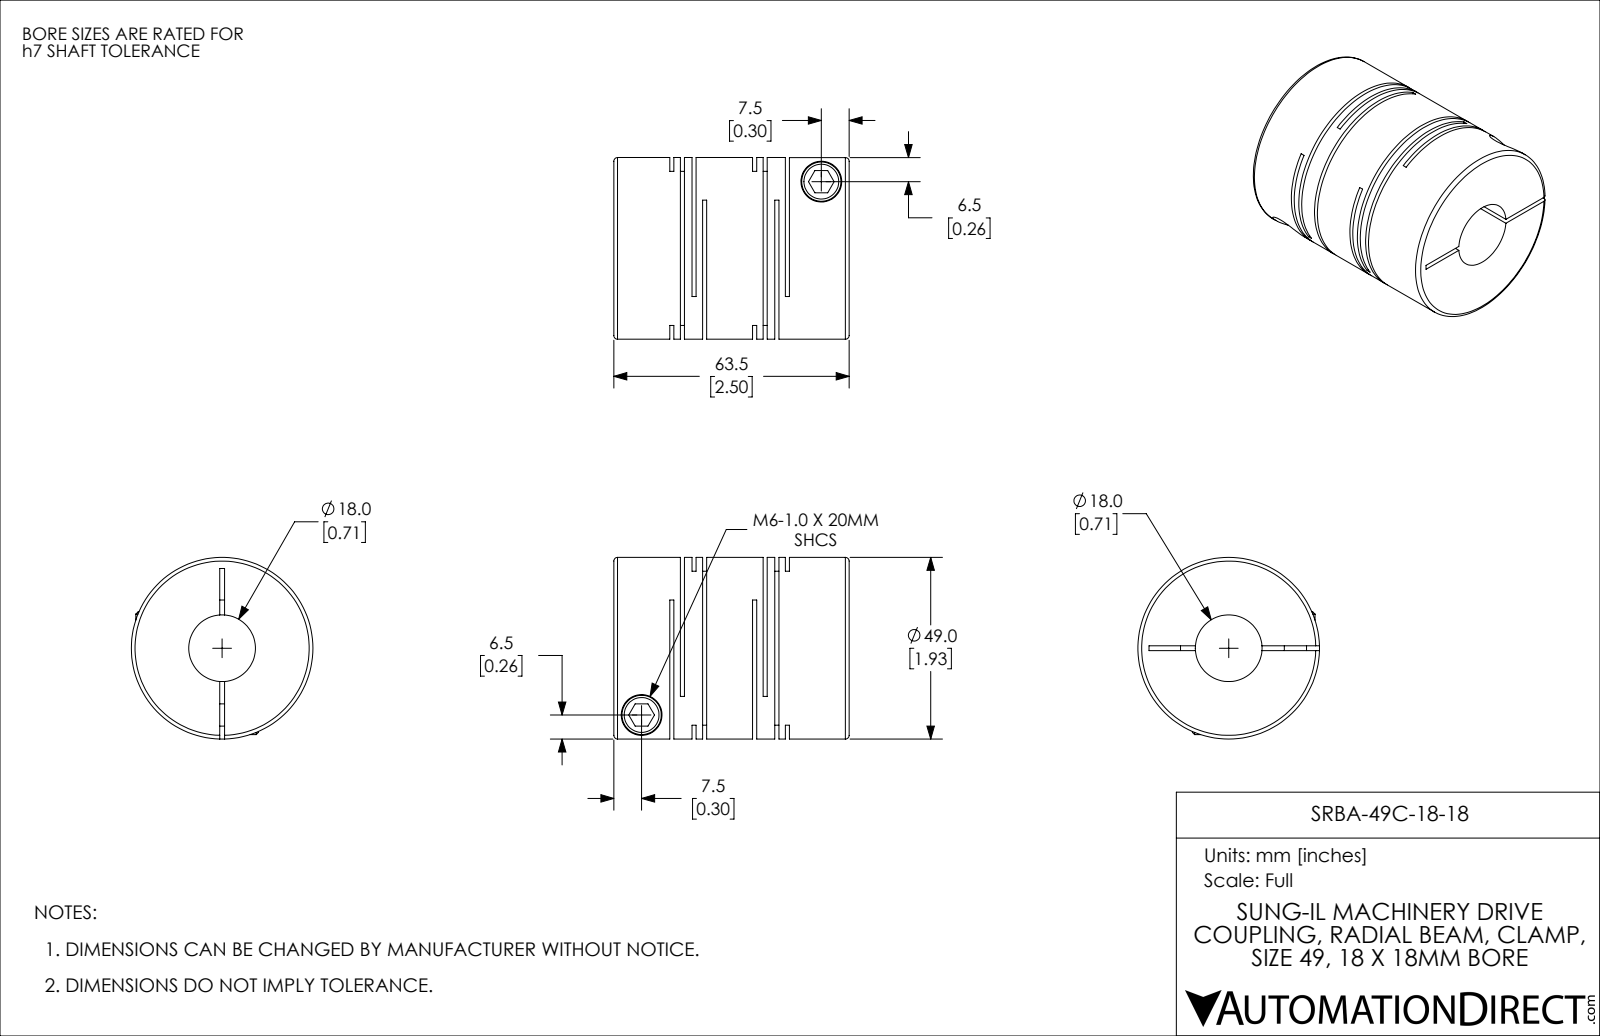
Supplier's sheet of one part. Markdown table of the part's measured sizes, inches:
| quantity | value |
| --- | --- |
| part name | SRBA-49C-18-18 |
| STEP written by | SolidWorks 2021 (CONFIG_CONTROL_DESIGN) |
| units | inches |
| bodies | 1 solid, 114 faces (60 planar, 42 cylindrical, 12 other) |
| overall size | 2.5 × 1.929 × 1.929 |
| volume | 5.456 in³ |
| surface area | 60.16 in² |
| round holes (diameter × count) | 0.236 × 2, 0.433 × 2, 0.709 × 1 |
| round bosses / shafts (diameter × count) | 0.417 × 2, 1.929 × 1 |
| main face-to-face distances | 0.236, 0.043, 0.112, 0.88, 0.193, 0.837, 0.124, 0.768, 0.644, 0.069 |
